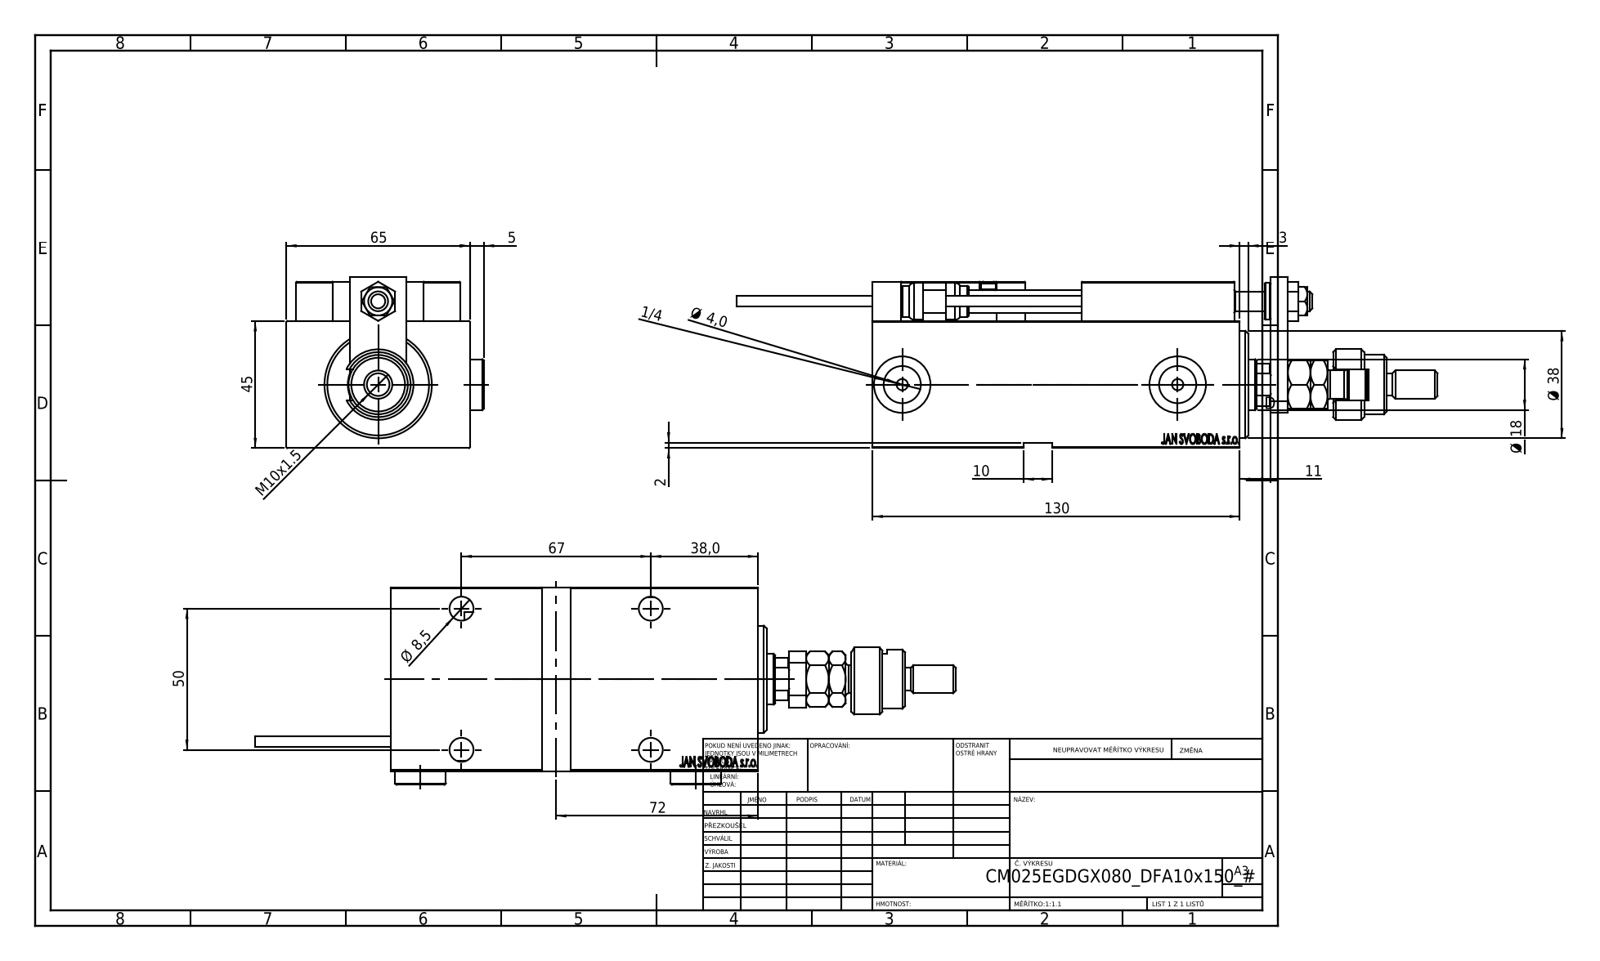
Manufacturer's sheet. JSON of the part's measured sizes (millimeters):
{"part_name": "ALLEN BOLT D5; NUT_D12; V450CM_E_VCP; SWITCH_X_FRONT_BACK (+7 more)", "step_written_by": "SolidWorks 2019 (CONFIG_CONTROL_DESIGN)", "units": "millimeters", "bodies": {"solids": 28, "faces": 1432, "planar": 632, "cylindrical": 211, "other": 589}, "overall_size": [248, 69.9, 60.5], "volume_mm3": 406656, "surface_area_mm2": 98430, "round_holes": [[4, 6], [8, 5], [8.5, 5], [3.2, 4], [13.5, 4], [5, 2], [13.16, 2], [20, 2], [7, 1], [14.5, 1], [18, 1], [21.5, 1]], "round_bosses_or_shafts": [[18, 2], [5, 2], [3.8, 2], [38, 1], [27, 1], [25, 1], [21, 1], [16, 1]], "partial_cylinders_radius": [[0.3, 30], [3, 2], [5.5, 1], [8.5, 1], [8.75, 1]], "face_to_face_distances": [45, 65, 14, 6, 59, 13, 130, 5, 19, 141], "hole_center_spacings": [40.31, 11.37, 20, 25, 29.59, 29.69, 34.44, 36.06]}
